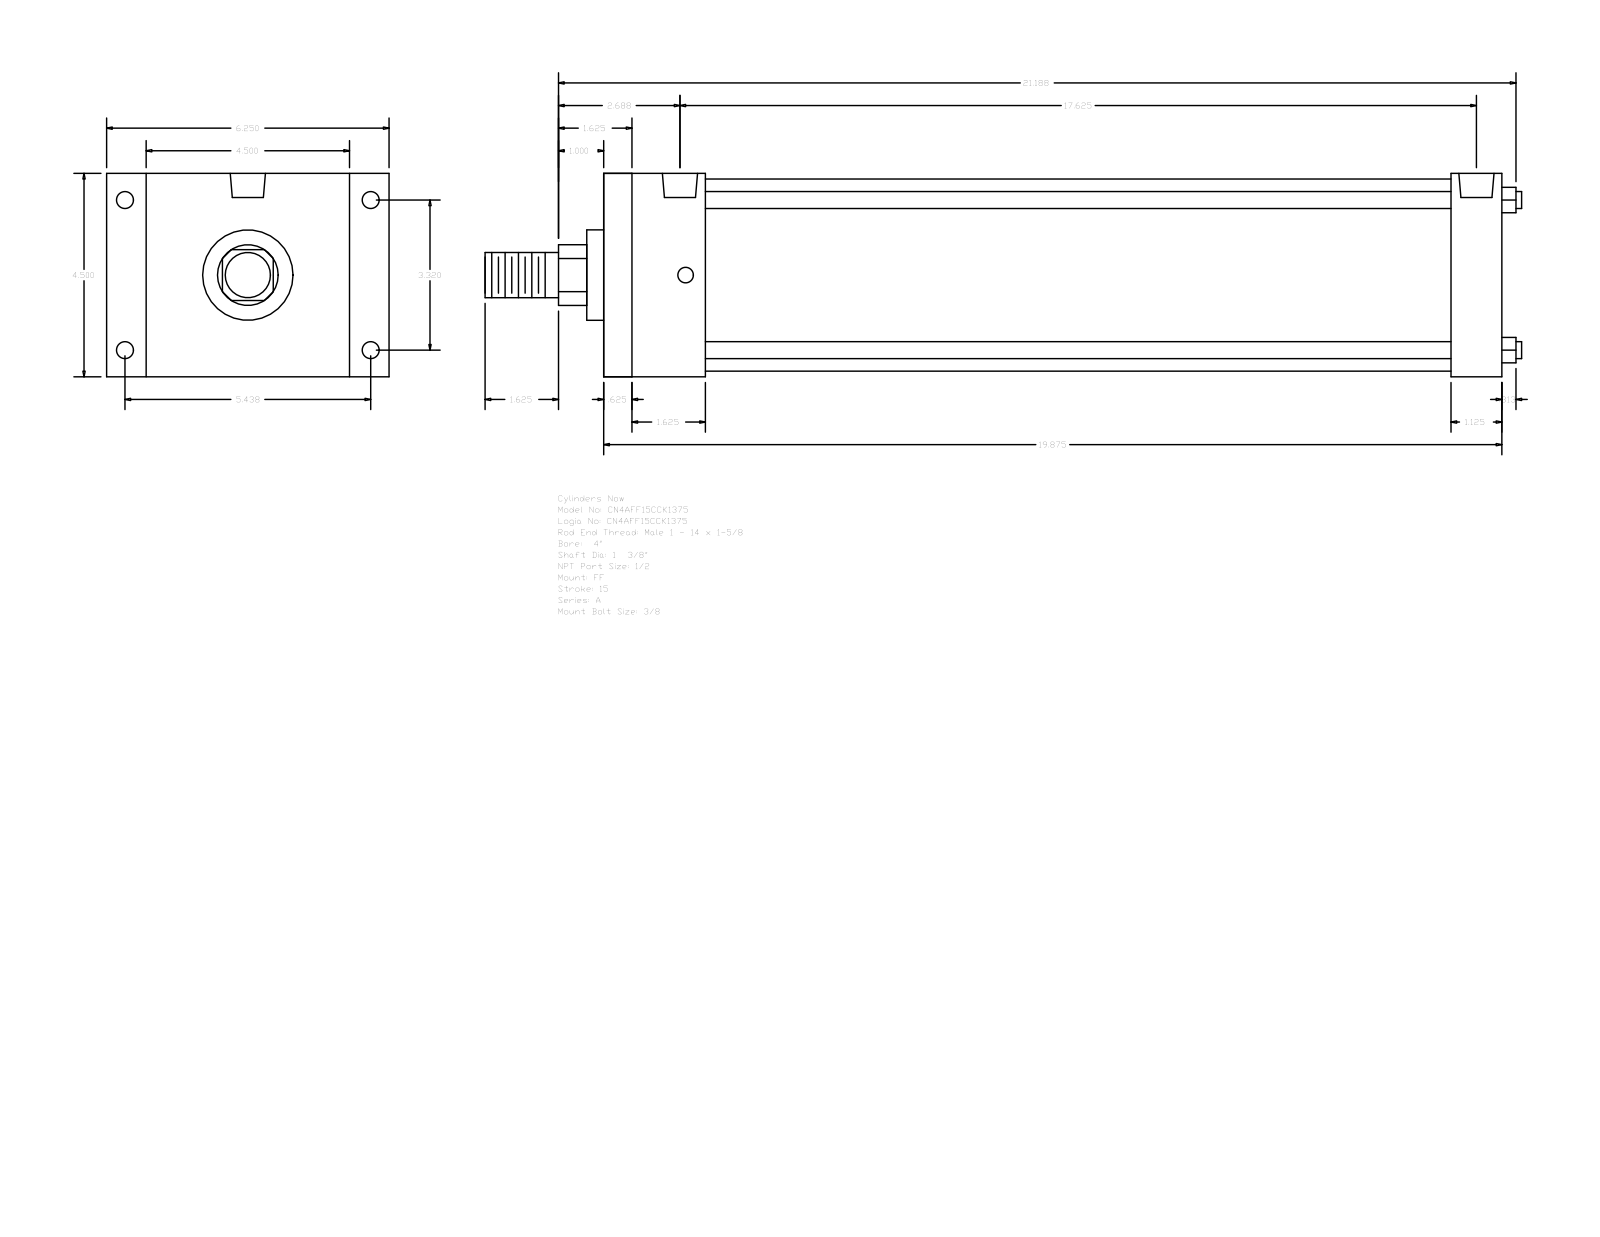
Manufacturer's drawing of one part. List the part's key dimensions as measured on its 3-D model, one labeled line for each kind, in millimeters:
Part name (STEP PRODUCT): A_FF__0400_1.375
STEP written by: GSSL Pune (CONFIG_CONTROL_DESIGN)
Units: millimetres
Bodies: 0 solids, 92 faces (64 planar, 28 cylindrical, 0 other)
Overall size (bounding box): 582.61 × 158.75 × 114.3
Round holes (diameter × count): ⌀8.73 ×4, ⌀9.53 ×4, ⌀19.77 ×2
Round bosses / shafts (diameter × count): ⌀9.53 ×4, ⌀107.95 ×1, ⌀50.8 ×1, ⌀34.92 ×1, ⌀25.4 ×1
Partial cylindrical surfaces — rounded edges, fillets, slot ends (radius × count): R17.06 ×1
Main face-to-face distances: 114.3, 504.83, 15.87, 488.96, 57.15, 28.58, 22.23, 136.53, 476.25, 460.38
Hole centre spacings: 3.18, 84.32, 138.12, 161.82, 441.32, 444.5, 447.68
